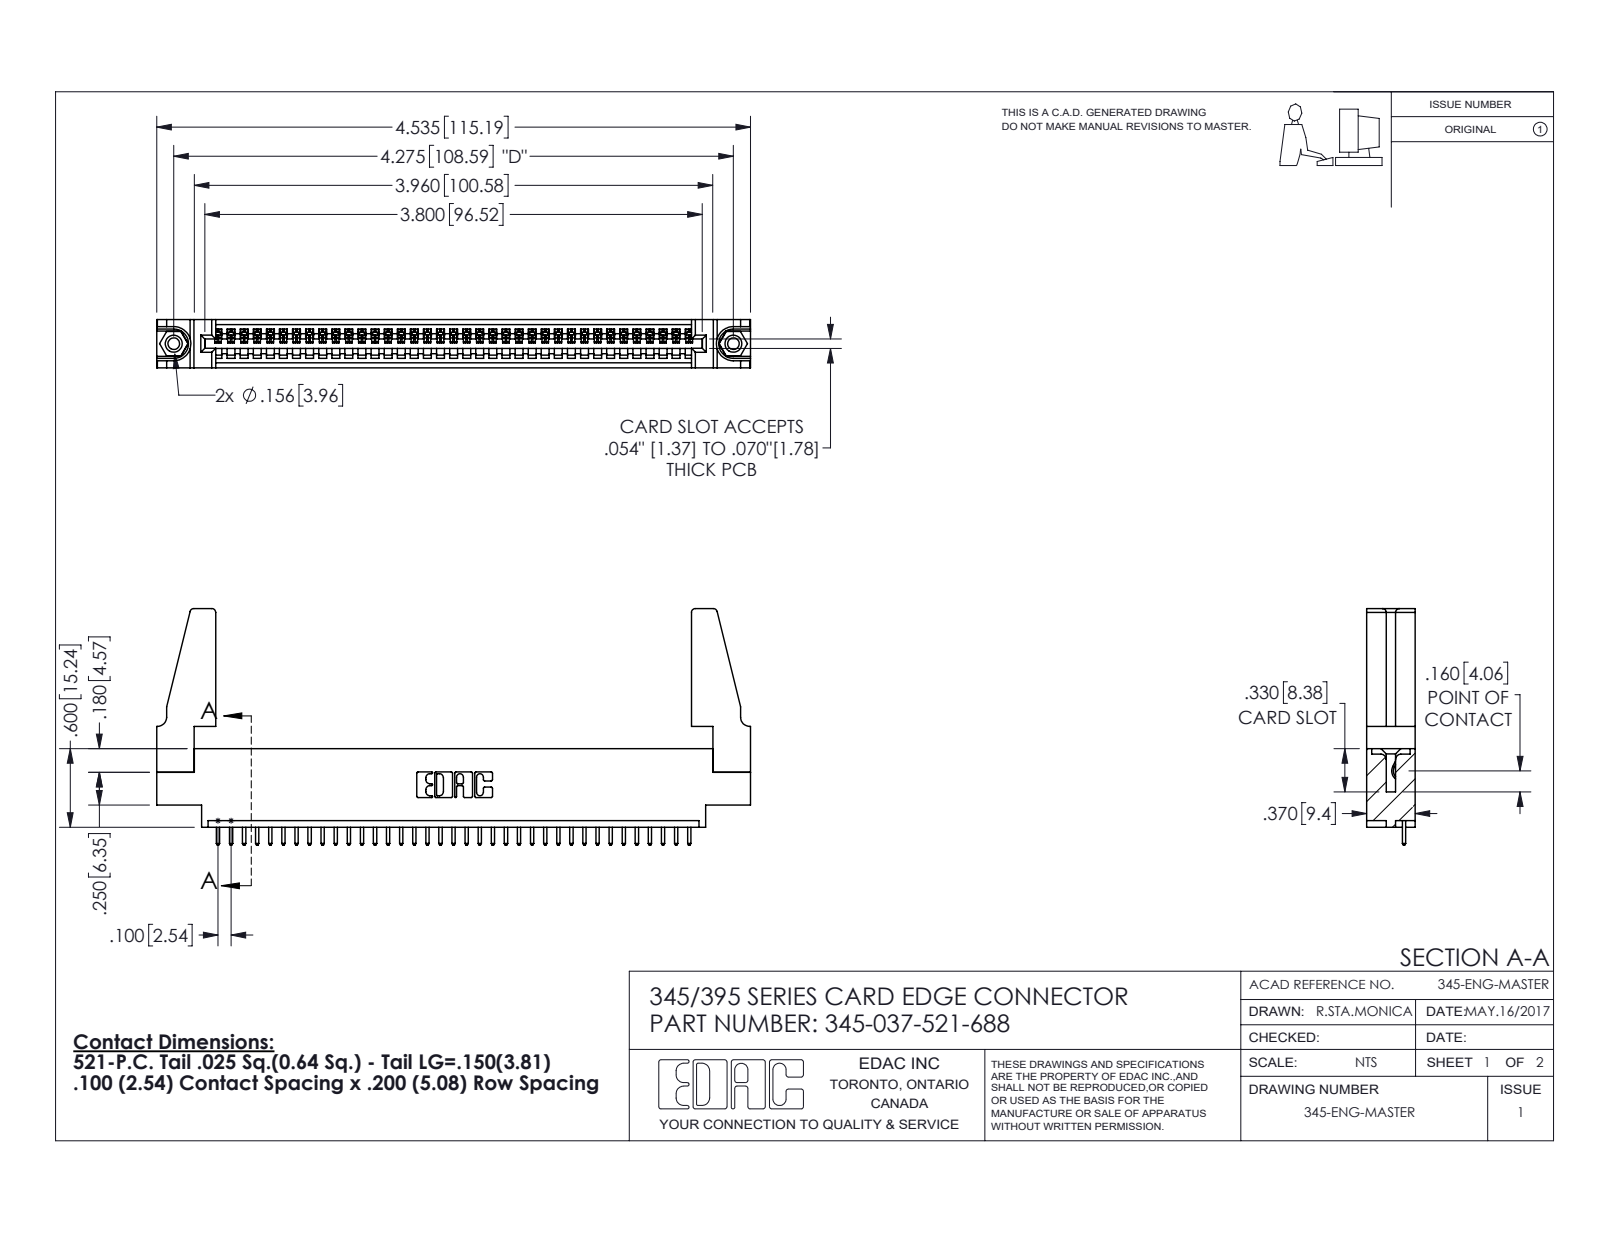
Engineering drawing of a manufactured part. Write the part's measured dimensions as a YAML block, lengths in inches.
part_name: "345-292-001_345-293-121; 345-037-521-688; 345-220-078_345-220-088; 345-250-001_345-250-001-102 (+1 more)"
step_written_by: "SolidWorks 2016 (CONFIG_CONTROL_DESIGN)"
units: inches
bodies: {solids: 42, faces: 2400, planar: 1636, cylindrical: 748, other: 16}
overall_size: [4.536, 1.807, 0.37]
volume: 0.85
surface_area: 26.31
round_holes:
  - {diameter: 0.089, count: 2}
  - {diameter: 0.125, count: 2}
  - {diameter: 0.156, count: 2}
  - {diameter: 0.064, count: 1}
round_bosses_or_shafts:
  - {diameter: 0.155, count: 2}
partial_cylinders:
  - {radius: 0.006, count: 74}
  - {radius: 0.01, count: 74}
  - {radius: 0.01, count: 22}
  - {radius: 0.03, count: 8}
  - {radius: 0.007, count: 6}
  - {radius: 0.031, count: 6}
  - {radius: 0.026, count: 3}
  - {radius: 0.031, count: 2}
face_to_face_distances: [0.37, 0.072, 0.298, 0.098, 0.272, 0.025, 0.2, 0.225, 0.175, 0.149]
hole_center_spacings: [0.27, 4.039, 4.275]
